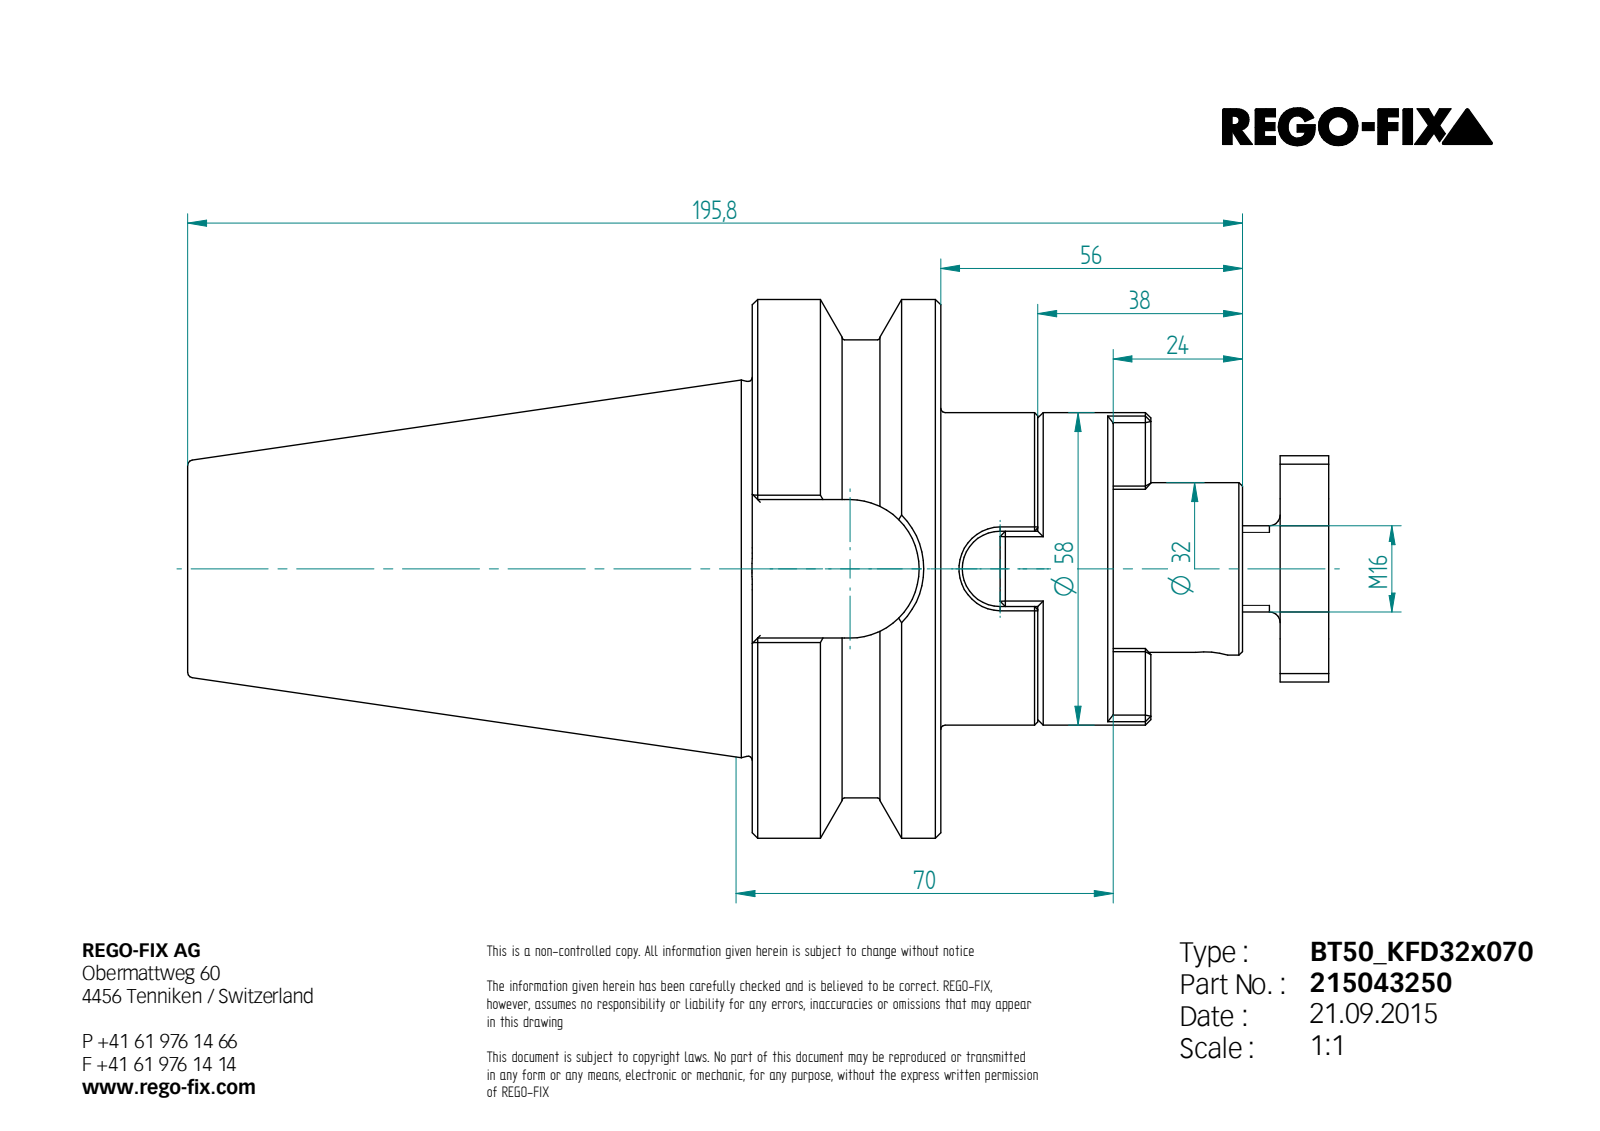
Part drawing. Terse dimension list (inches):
written by: Unknown (AUTOMOTIVE_DESIGN)
unit: in
bodies: 3 solids, 207 faces (118 planar, 35 cylindrical, 54 other)
size: 8.339 × 3.937 × 3.937
volume: 33.75 in³; area: 119.4 in²
holes: 1× ⌀0.545, 1× ⌀0.669, 1× ⌀0.817, 1× ⌀0.984, 1× ⌀1.26
bosses: 1× ⌀3.937, 1× ⌀3.346, 1× ⌀2.283, 1× ⌀1.236, 1× ⌀0.63
rounds: 4× R0.02, 4× R0.197, 2× R0.157, 1× R0.276, 1× R0.506, 1× R0.827
face distances: 1.378, 0.709, 2.087, 0.551, 2.638, 1.26, 2.835, 4.213, 2.126, 1.575
